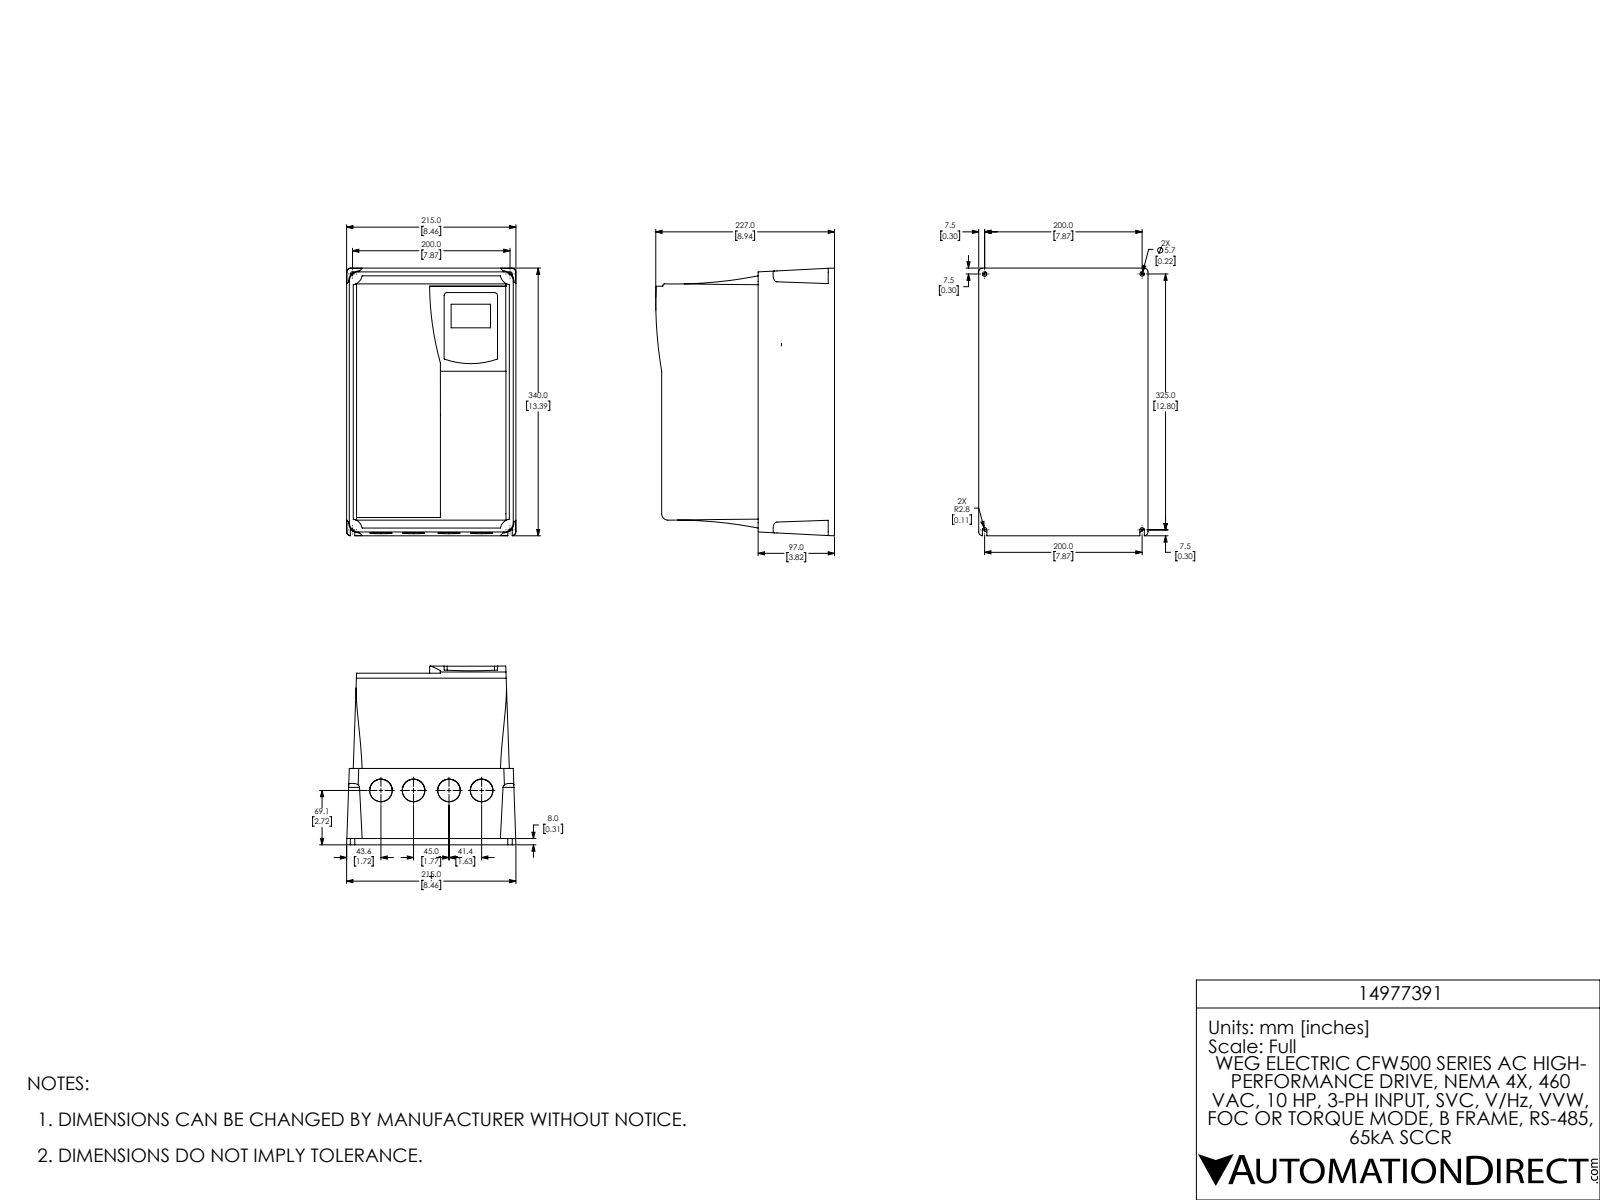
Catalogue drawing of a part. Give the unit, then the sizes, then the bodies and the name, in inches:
Units: inches
Overall size (bounding box): 13.386 × 8.937 × 8.465
Round holes (diameter × count): ⌀1.126 ×4, ⌀0.223 ×2
Partial cylindrical surfaces — rounded edges, fillets, slot ends (radius × count): R0.197 ×6, R0.472 ×4, R0.551 ×4, R0.033 ×2, R0.111 ×2, R0.152 ×2, R0.079 ×1, R0.315 ×1
Main face-to-face distances: 0.196, 8.583, 8.642, 0.059, 3.819, 4.764, 4.823, 14.335, 0.118, 8.602
Hole centre spacings: 1.63, 3.402, 1.772, 5.032, 7.874
Volume: 858 in³ · Surface area: 565.3 in²
Bodies: 1 solid, 82 faces (40 planar, 40 cylindrical, 2 other)
Part name (STEP PRODUCT): CFW500 MEC-B IP66 - SEM SECCIONADORA Coord
STEP written by: SolidWorks 2017 (AUTOMOTIVE_DESIGN)
